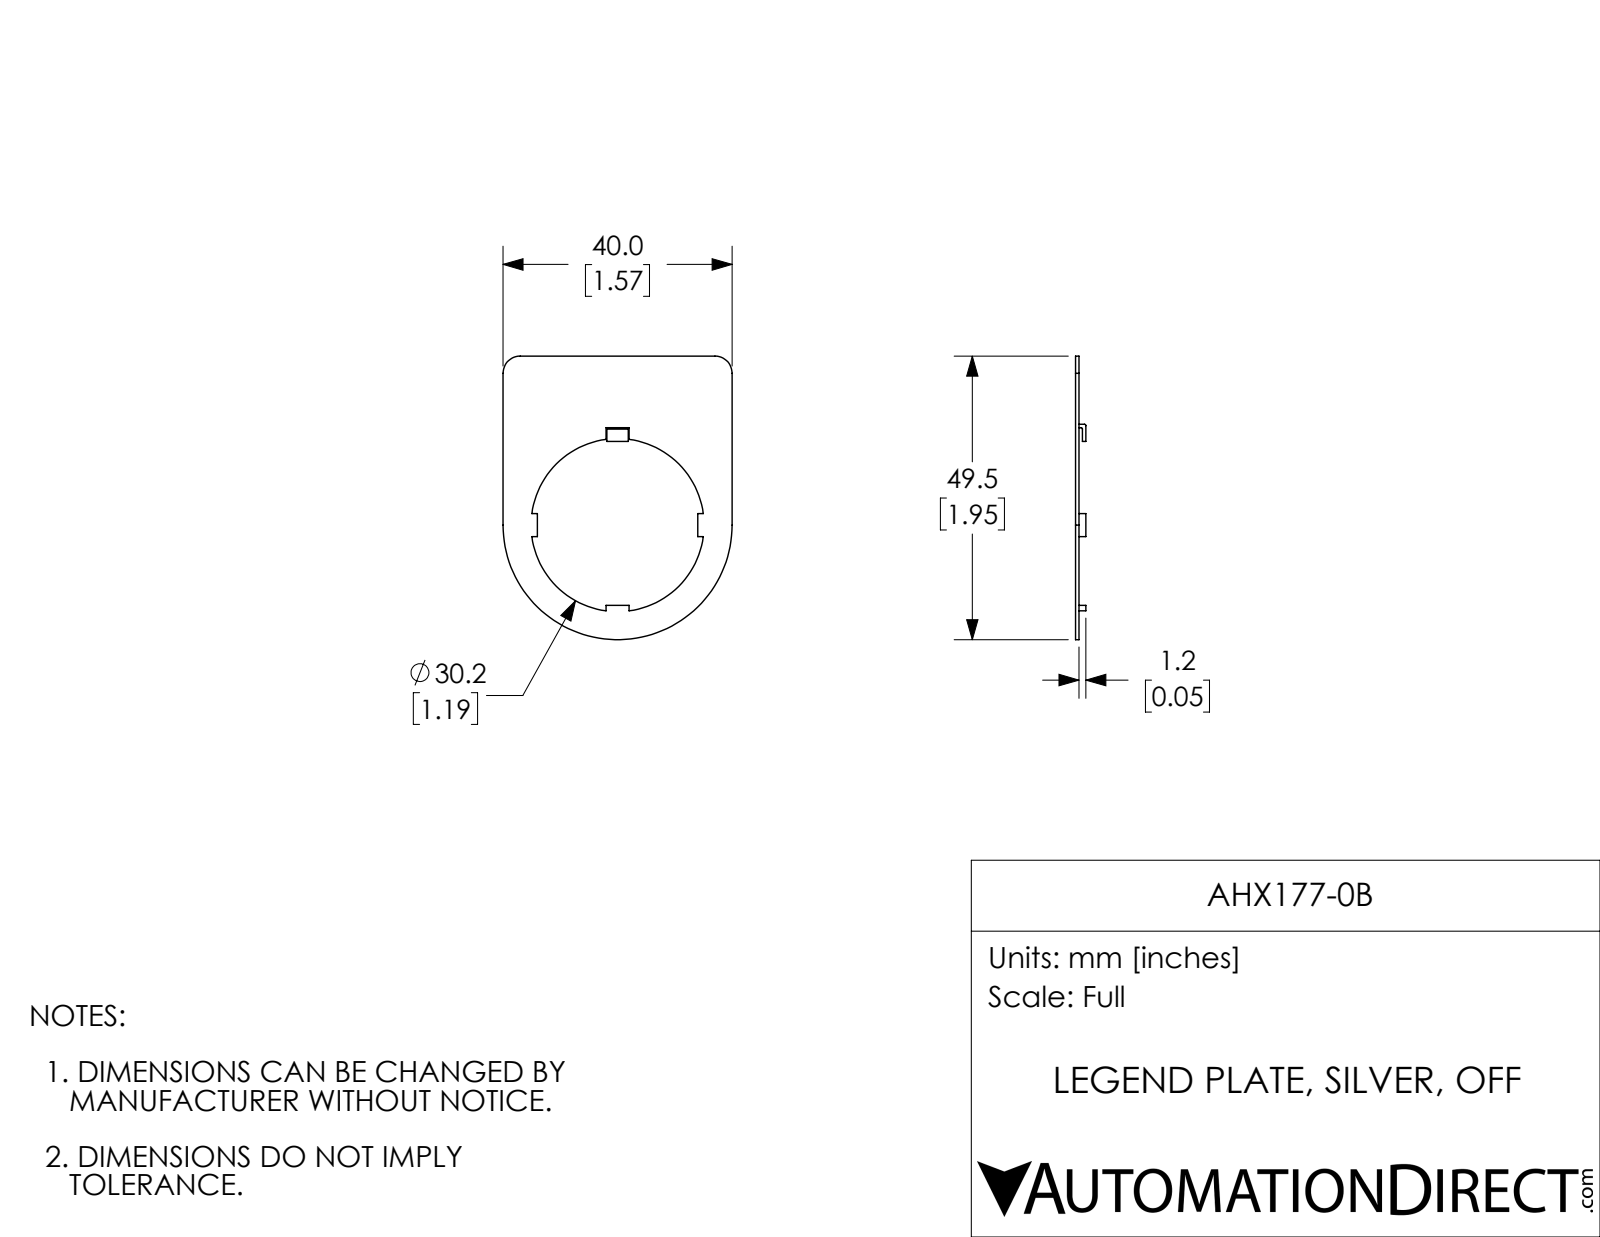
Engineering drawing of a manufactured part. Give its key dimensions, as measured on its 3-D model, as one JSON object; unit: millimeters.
{"part_name": "AHX177-0B", "step_written_by": "SolidWorks 2017 (AUTOMOTIVE_DESIGN)", "units": "millimeters", "bodies": {"solids": 1, "faces": 38, "planar": 29, "cylindrical": 9, "other": 0}, "overall_size": [49.5, 40, 1.8], "volume_mm3": 670, "surface_area_mm2": 2410, "round_holes": [[30.2, 1]], "partial_cylinders_radius": [[0.3, 2], [3, 2], [20, 1]], "face_to_face_distances": [0.6, 1.2, 1.8, 40, 1, 6, 34, 5, 35, 29]}
